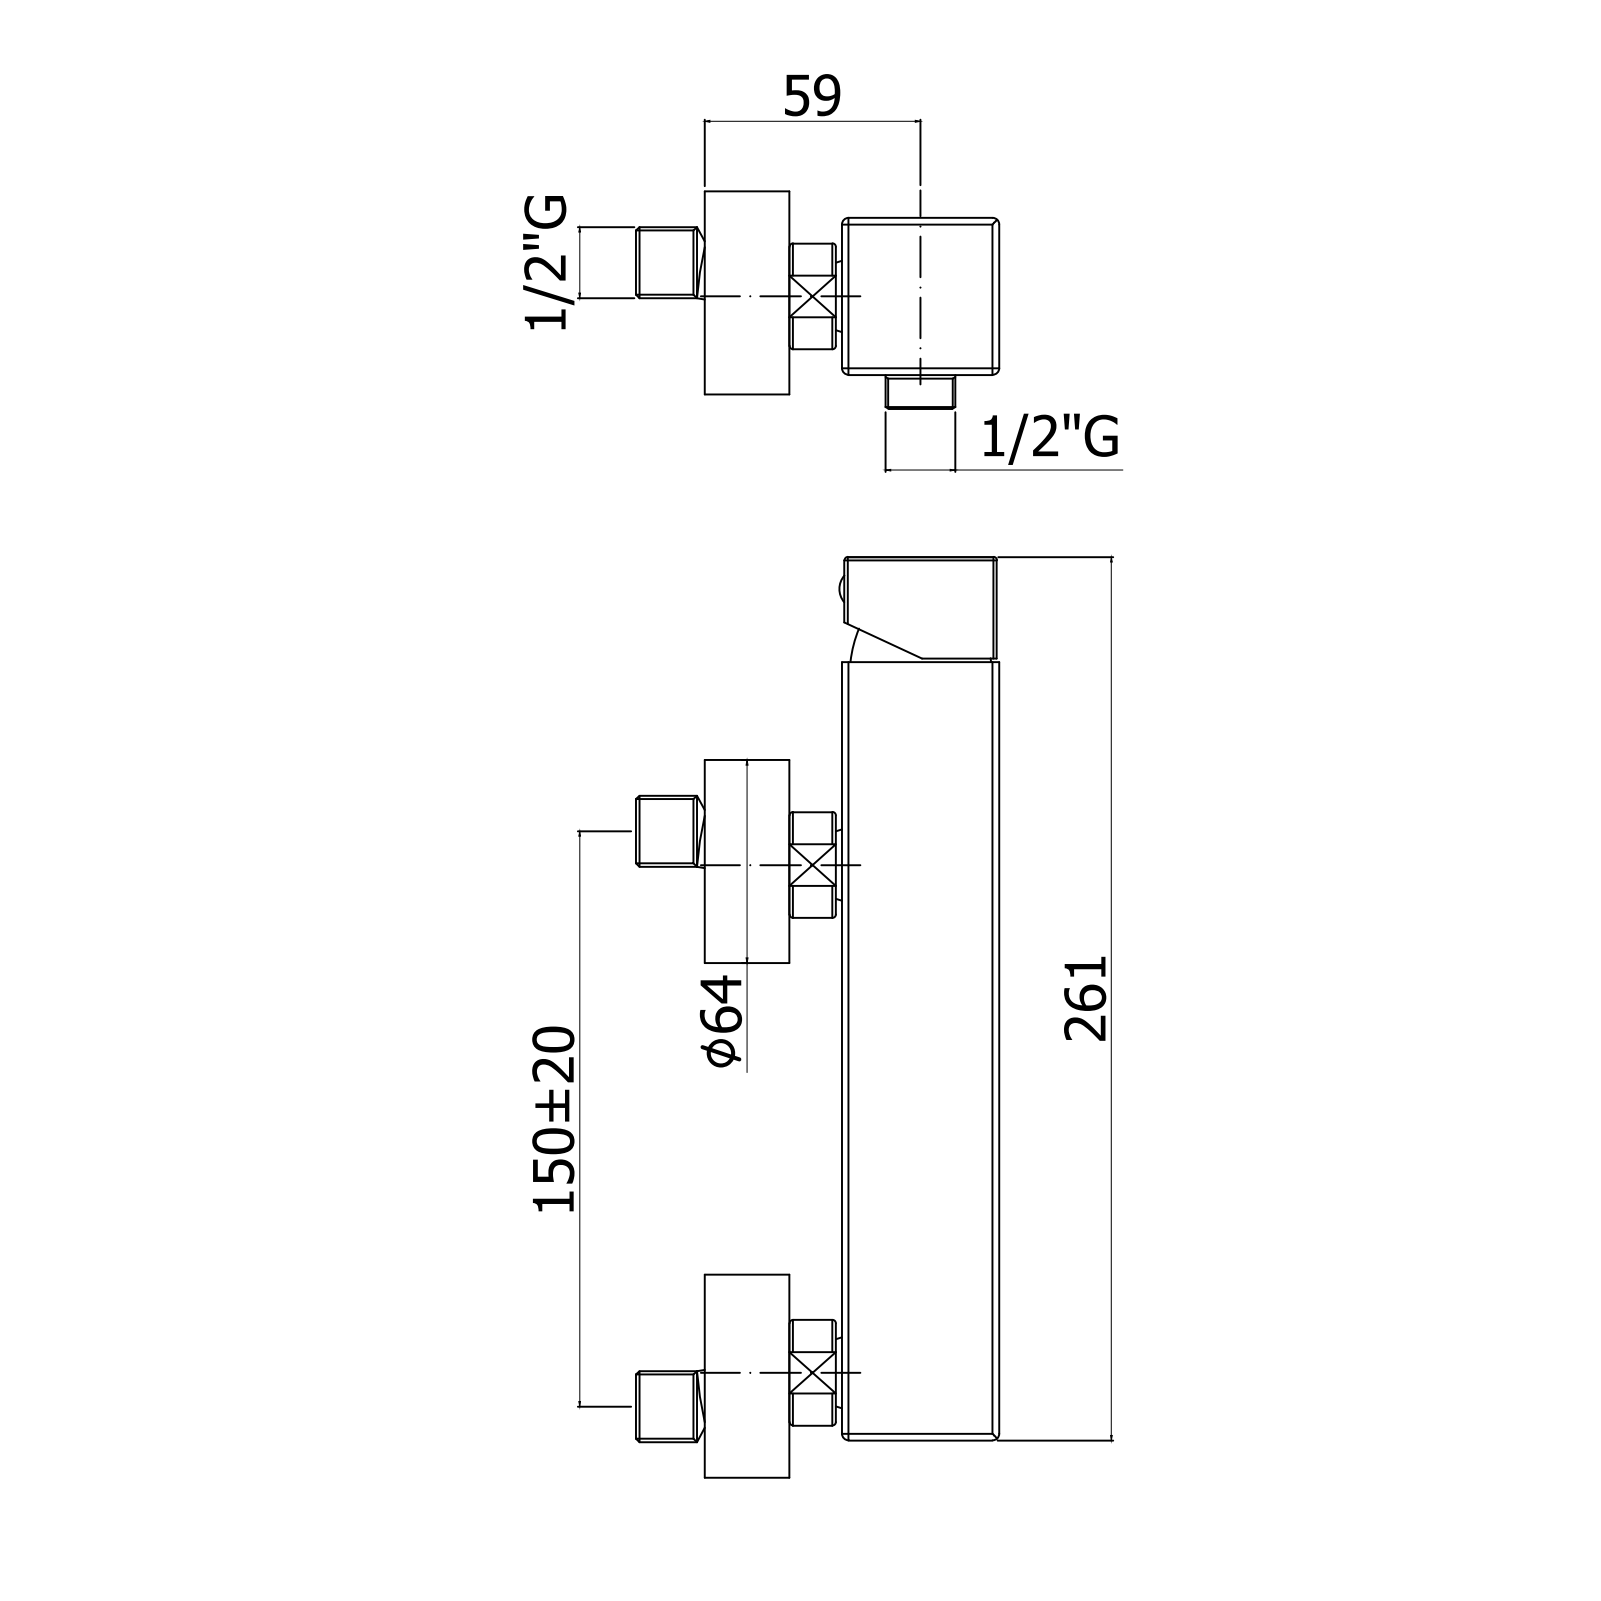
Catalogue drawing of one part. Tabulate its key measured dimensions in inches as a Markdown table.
| quantity | value |
| --- | --- |
| part name | LEC168CR |
| STEP written by | CREO PARAMETRIC BY PTC INC, 2020044 (CONFIG_CONTROL_DESIGN) |
| units | inches |
| bodies | 1 solid, 1528 faces (741 planar, 459 cylindrical, 328 other) |
| overall size | 10.738 × 3.209 × 2.618 |
| volume | 16.09 in³ |
| surface area | 261.4 in² |
| round holes (diameter × count) | 0.472 × 4, 0.354 × 3, 0.157 × 2, 0.276 × 2, 0.315 × 2, 0.413 × 2, 0.709 × 2, 0.85 × 2, 0.965 × 2, 0.984 × 2, 1.457 × 2, 2.453 × 2 |
| round bosses / shafts (diameter × count) | 2.5 × 2, 1.063 × 2, 0.945 × 2, 0.697 × 2, 1.378 × 1, 1.37 × 1, 1.331 × 1, 1.268 × 1 |
| partial cylindrical surfaces (radius × count) | 0.039 × 98, 0.02 × 44, 0.006 × 11, 0.012 × 9, 0.059 × 4, 0.276 × 4, 0.177 × 2, 0.197 × 2 |
| main face-to-face distances | 0.148, 1.683, 1.831, 1.535, 0.118, 0.591, 0.738, 2.274, 2.421, 0.024 |
| hole center spacings | 0.028, 0.335, 0.339, 0.513, 0.52, 0.532, 0.236, 0.512 |
